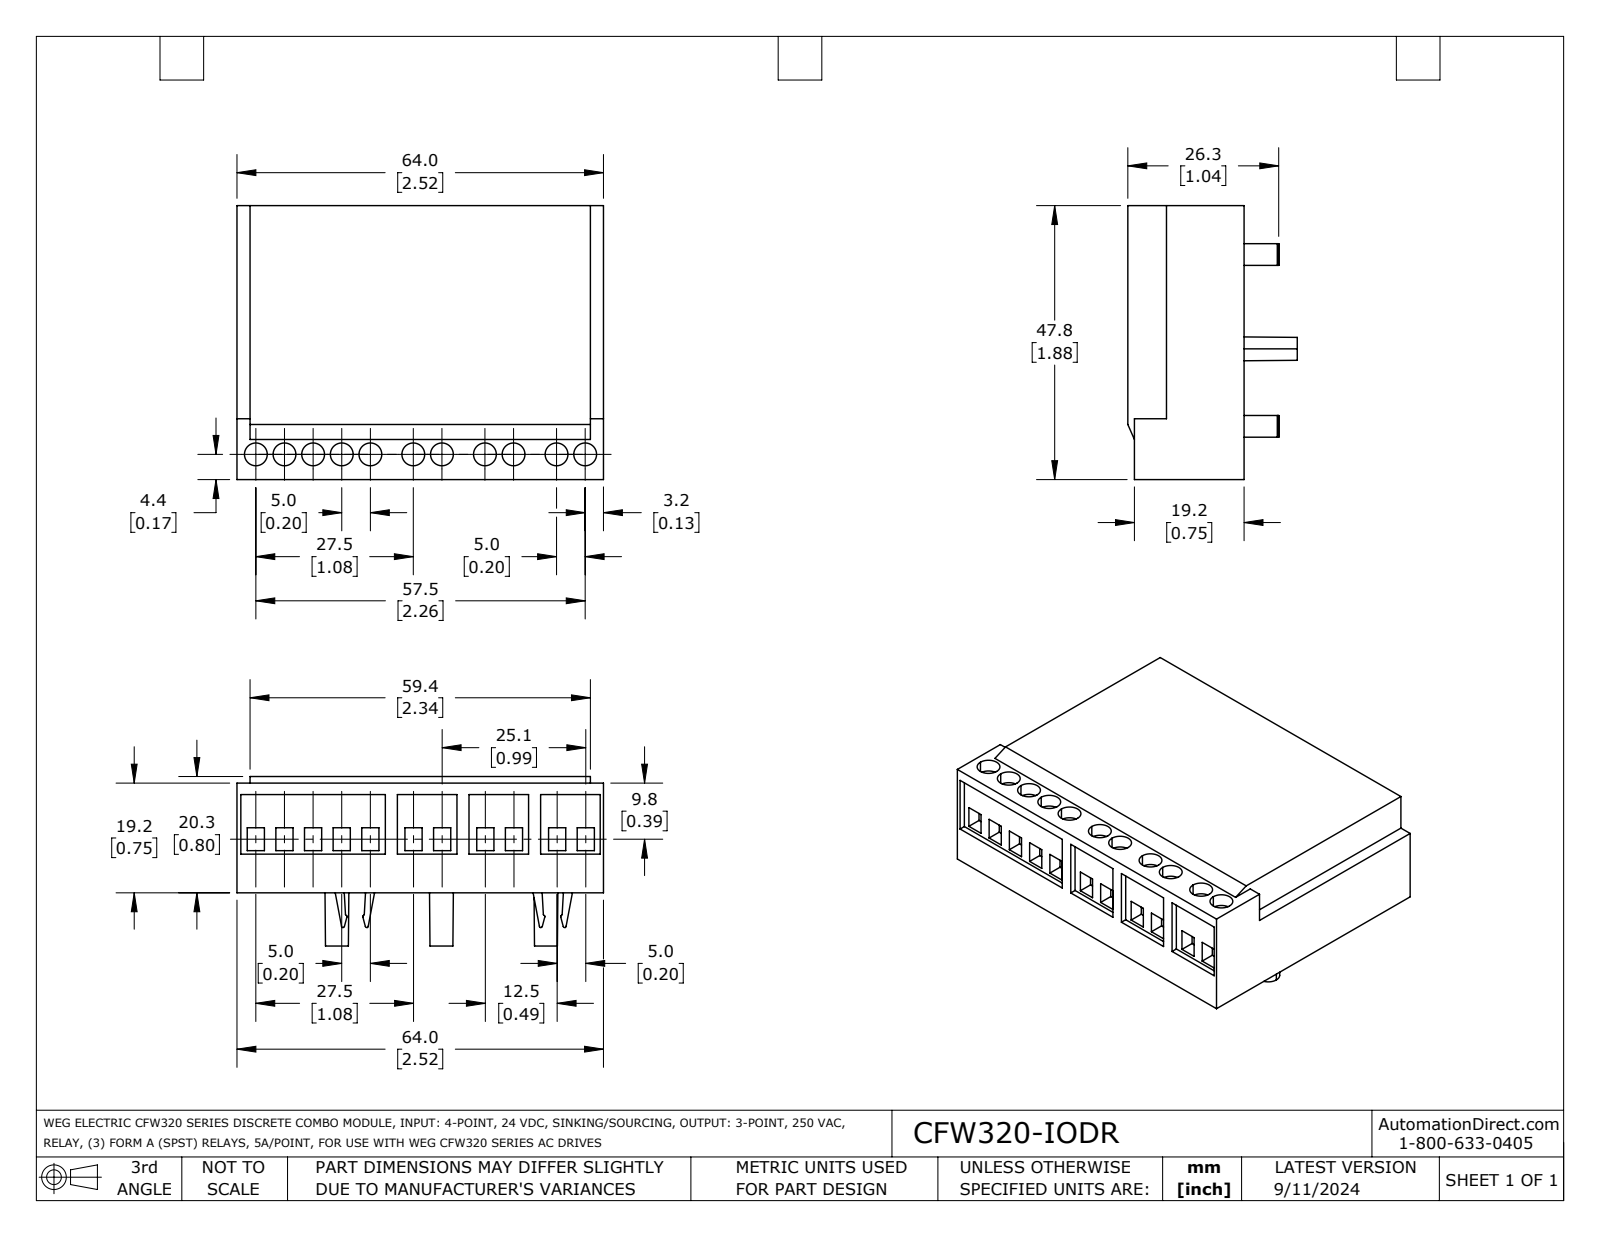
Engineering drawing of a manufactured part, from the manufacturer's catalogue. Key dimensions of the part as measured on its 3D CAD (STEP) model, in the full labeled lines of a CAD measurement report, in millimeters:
Part name (STEP PRODUCT): CFW320 IODR
STEP written by: SolidWorks 2021 (AUTOMOTIVE_DESIGN)
Units: millimetres
Bodies: 1 solid, 206 faces (162 planar, 22 cylindrical, 22 other)
Overall size (bounding box): 64 × 47.8 × 29.6
Volume: 58 220 mm³ · Surface area: 12 290 mm²
Round holes (diameter × count): ⌀4 ×11
Main face-to-face distances: 20.3, 47.8, 64, 2.3, 61.7, 1.1, 46.8, 4.2, 16.1, 19.2
Hole centre spacings: 5, 12.5, 10, 7.5, 12.5, 15, 17.5, 17.5
